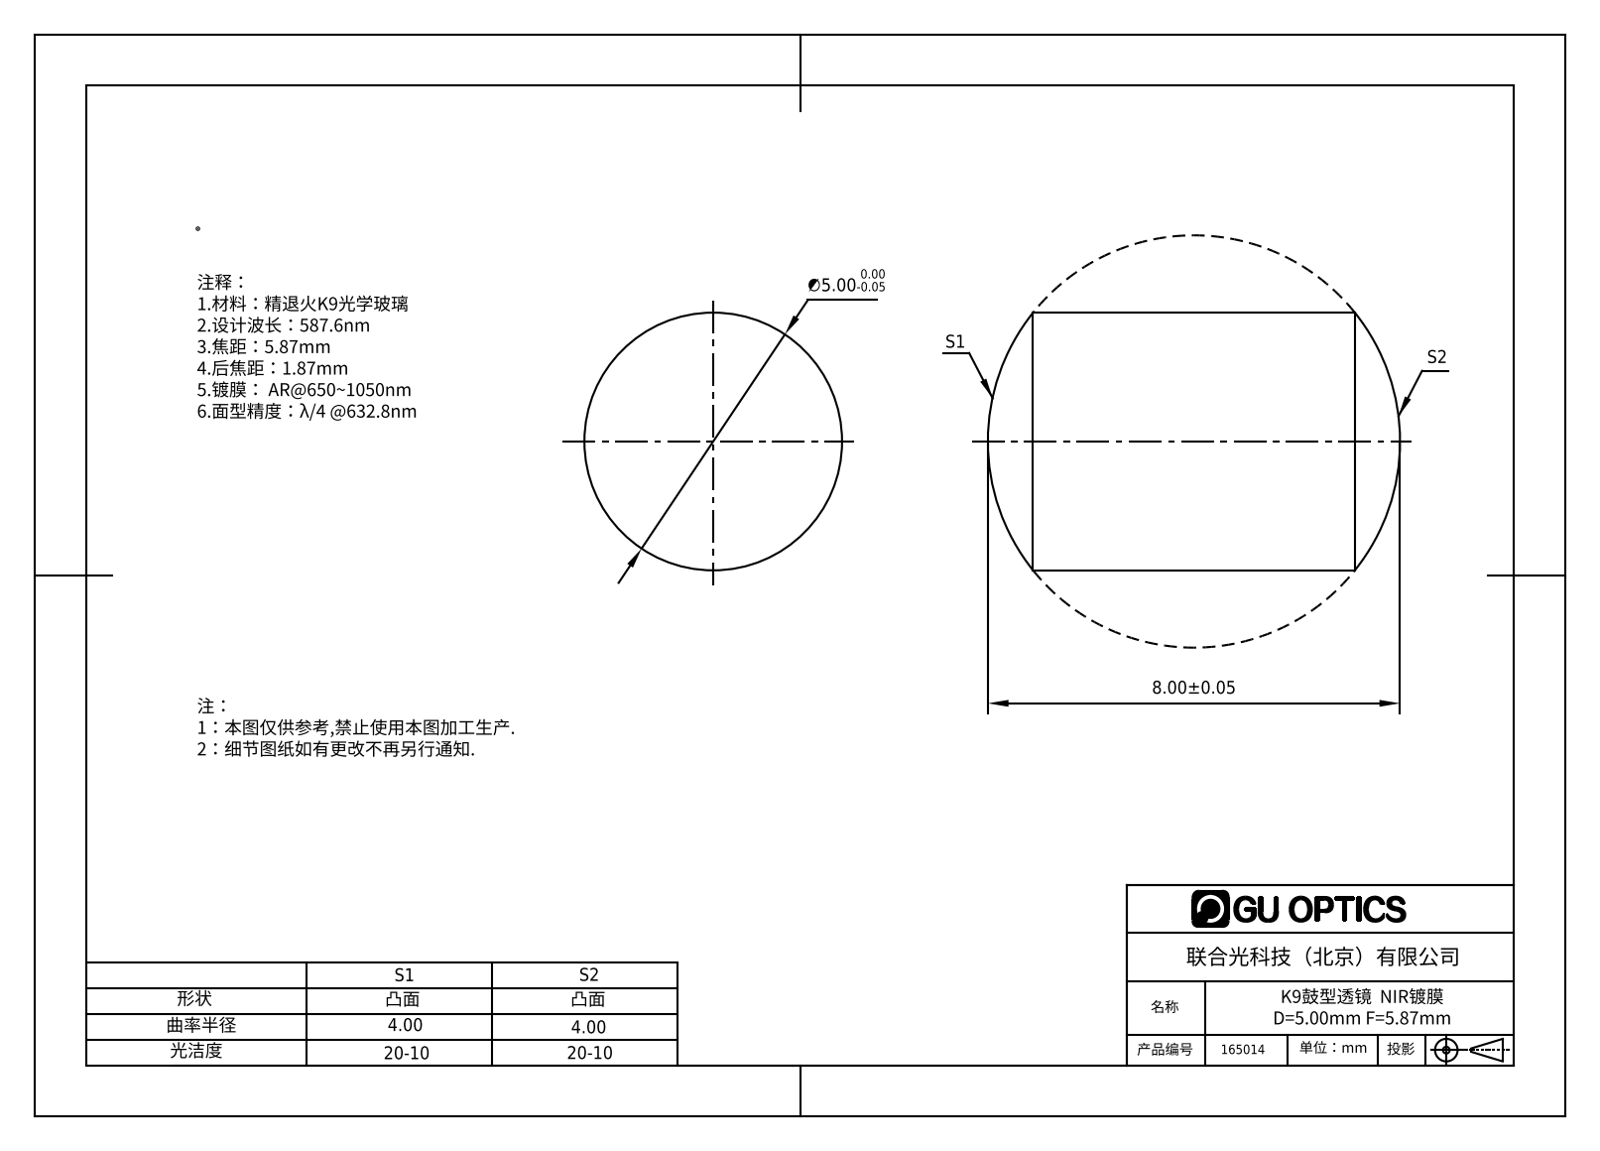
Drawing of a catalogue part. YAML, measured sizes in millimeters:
part_name: "165004"
step_written_by: "SolidWorks 2016 (CONFIG_CONTROL_DESIGN)"
units: millimeters
bodies: {solids: 1, faces: 6, planar: 0, cylindrical: 2, other: 4}
overall_size: [8, 5, 5]
volume: 141
surface_area: 142
round_bosses_or_shafts:
  - {diameter: 5, count: 1}
